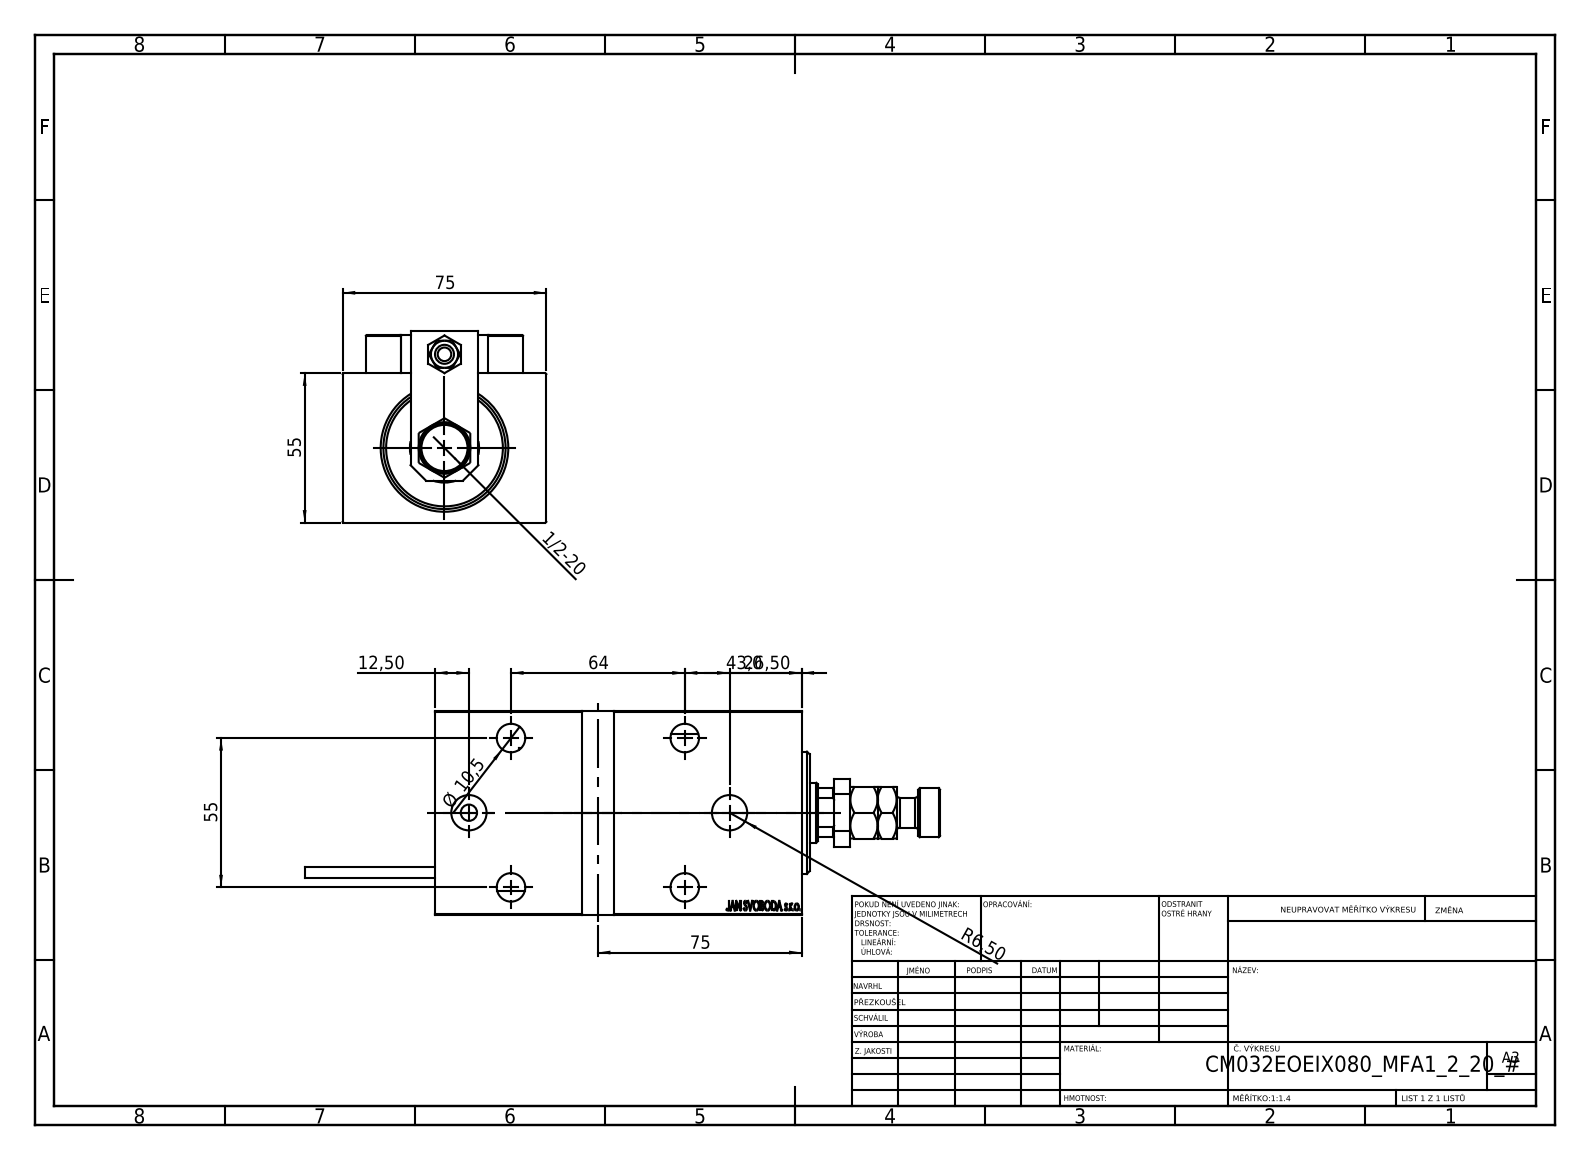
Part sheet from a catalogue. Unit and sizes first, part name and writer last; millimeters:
Units: millimetres
Overall size (bounding box): 234 × 75 × 70.5
Round holes (diameter × count): ⌀8 ×5, ⌀10.5 ×5, ⌀16.5 ×5, ⌀3.2 ×4, ⌀4 ×4, ⌀5 ×2, ⌀13 ×2, ⌀7 ×1, ⌀22 ×1, ⌀25.5 ×1, ⌀32 ×1, ⌀45 ×1
Round bosses / shafts (diameter × count): ⌀11 ×2, ⌀5 ×2, ⌀3.8 ×2, ⌀34 ×1, ⌀18 ×1, ⌀13 ×1, ⌀6 ×1
Partial cylindrical surfaces — rounded edges, fillets, slot ends (radius × count): R0.3 ×30, R3 ×2, R10.5 ×1
Main face-to-face distances: 55, 75, 3, 69, 10, 14, 135, 25, 12, 125
Hole centre spacings: 11.37, 12.5, 20, 21.91, 28.9, 29.59, 29.69, 31.57
Volume: 560 501 mm³ · Surface area: 111 653 mm²
Bodies: 25 solids, 1335 faces (584 planar, 178 cylindrical, 573 other)
Part name (STEP PRODUCT): NUT_D12; KONCOVKA; MAGNET; X_Y_MFA (+7 more)
STEP written by: SolidWorks 2019 (CONFIG_CONTROL_DESIGN)
